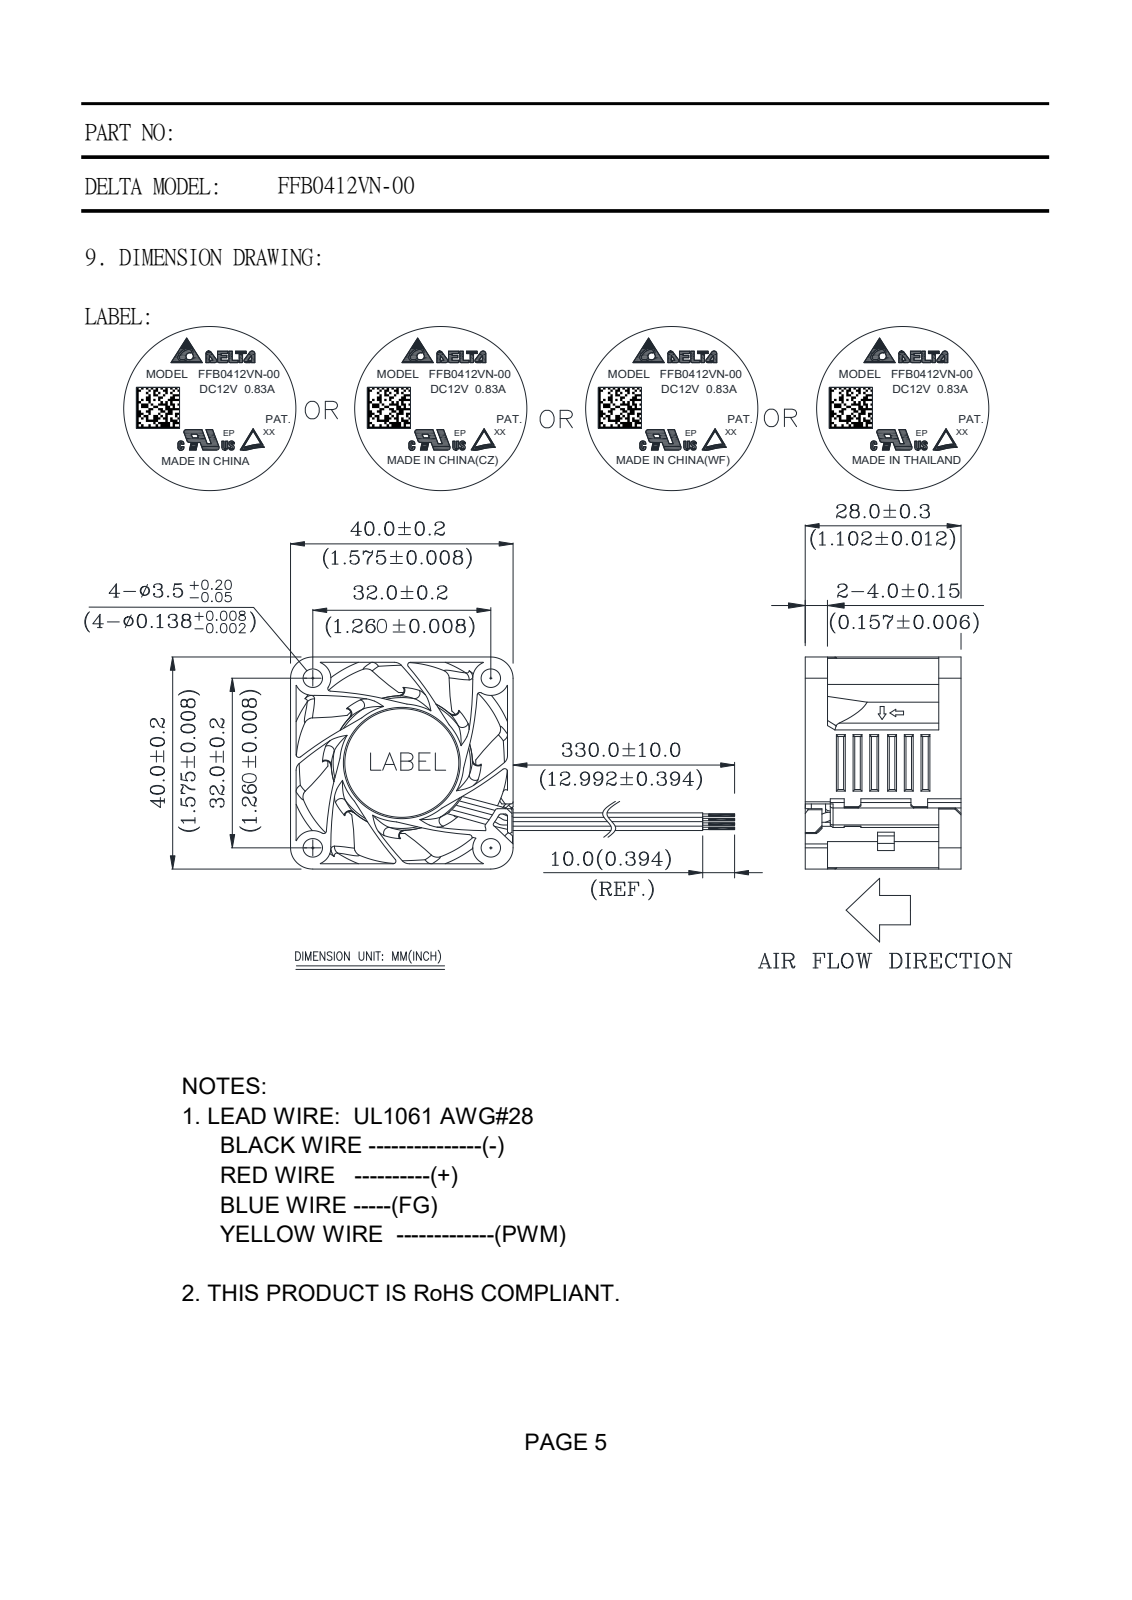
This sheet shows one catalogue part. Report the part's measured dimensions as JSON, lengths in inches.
{"part_name": "FFB0412VN-00", "step_written_by": "CREO PARAMETRIC BY PTC INC, 2015080 (CONFIG_CONTROL_DESIGN)", "units": "inches", "bodies": {"solids": 1, "faces": 836, "planar": 492, "cylindrical": 169, "other": 175}, "overall_size": [1.858, 1.858, 1.102], "volume_in3": 2.42, "surface_area_in2": 18.9, "round_holes": [[0.138, 4]], "round_bosses_or_shafts": [[1.496, 1]], "partial_cylinders_radius": [[0.012, 56], [0.079, 7], [0.008, 5], [0.016, 5], [0.02, 5], [0.126, 4], [0.128, 4], [0.148, 4]], "face_to_face_distances": [1.102, 1.576, 0.04, 1.536, 0.264, 0.02, 1.556, 0.02, 1.516, 0.157], "hole_center_spacings": [1.26, 1.782]}
